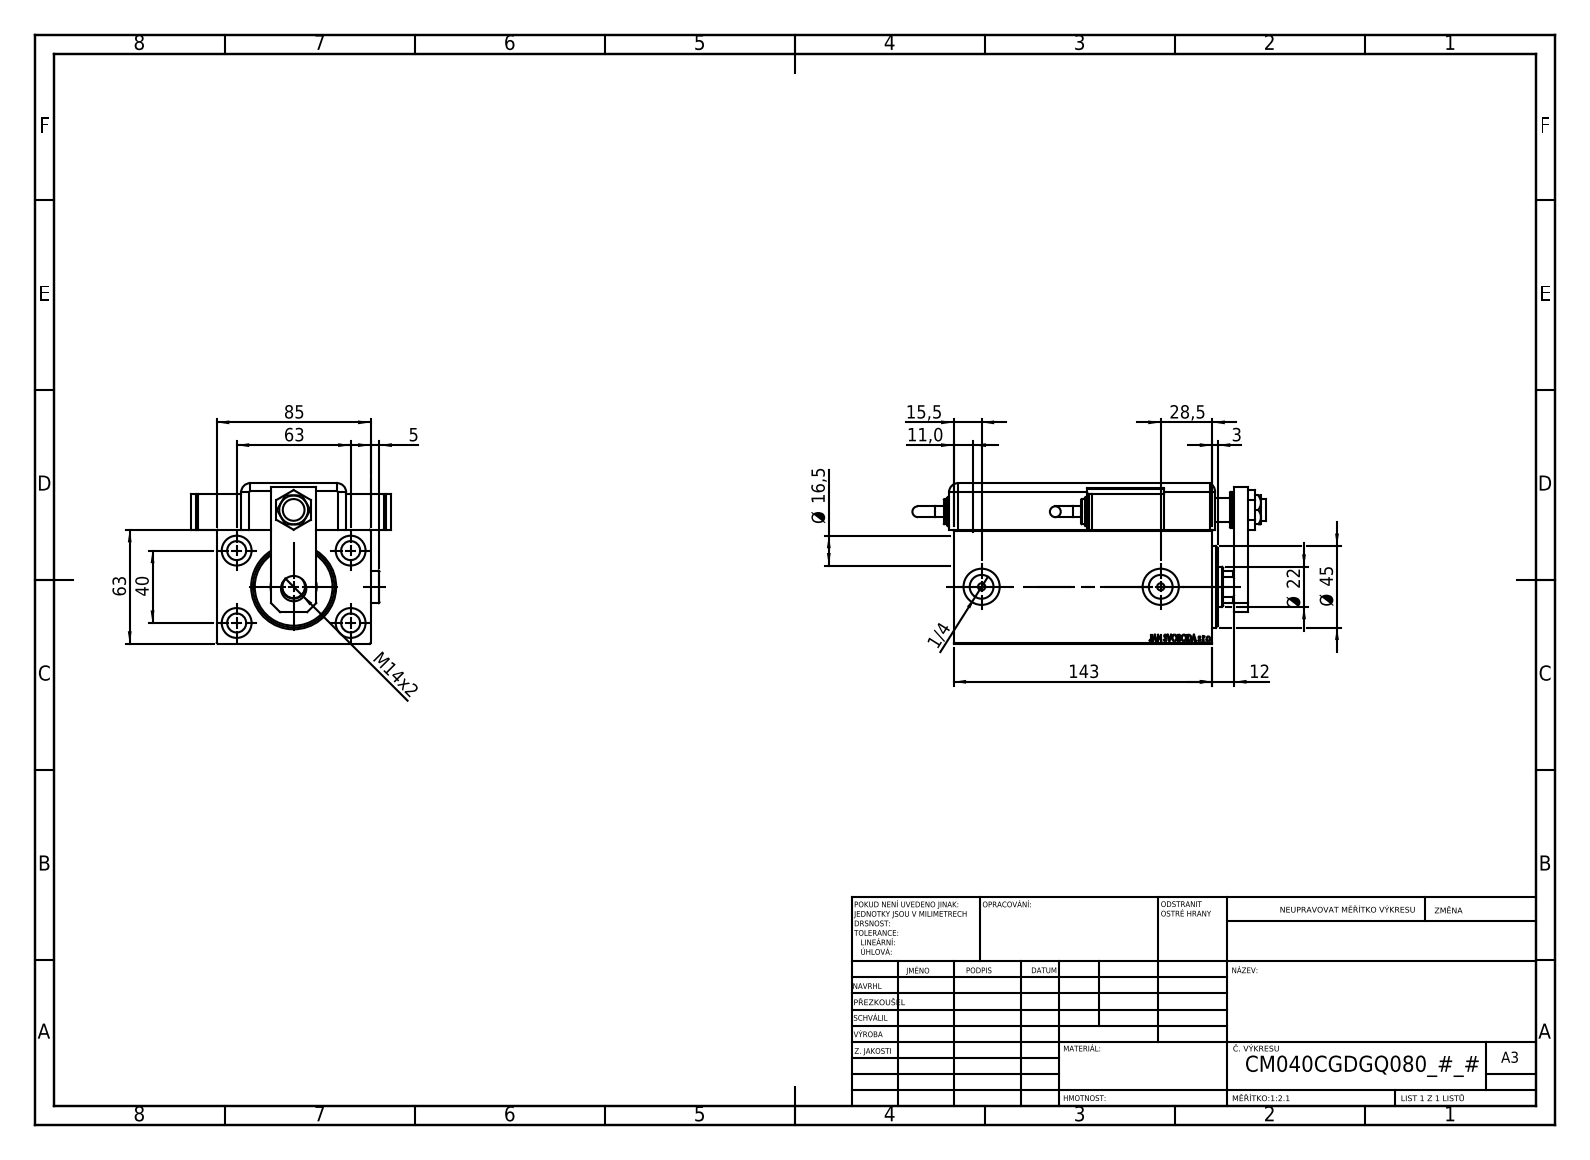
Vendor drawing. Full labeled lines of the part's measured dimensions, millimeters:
Part name (STEP PRODUCT): MAGNETIC SWITCH Q; TYC; V450CM_VC_B; SWITCH DIM A_G (+7 more)
STEP written by: SolidWorks 2019 (CONFIG_CONTROL_DESIGN)
Units: millimetres
Bodies: 15 solids, 1300 faces (648 planar, 131 cylindrical, 521 other)
Overall size (bounding box): 195.46 × 111 × 88.8
Volume: 793 620 mm³ · Surface area: 178 586 mm²
Round holes (diameter × count): ⌀4 ×4, ⌀10.5 ×4, ⌀16.5 ×4, ⌀8 ×2, ⌀13.16 ×2, ⌀14 ×2, ⌀20 ×2, ⌀12 ×1, ⌀12.5 ×1, ⌀13 ×1, ⌀22 ×1, ⌀25.5 ×1
Round bosses / shafts (diameter × count): ⌀20 ×3, ⌀18 ×2, ⌀16 ×2, ⌀14 ×2, ⌀6 ×2
Partial cylindrical surfaces — rounded edges, fillets, slot ends (radius × count): R5 ×9, R10 ×1, R10.5 ×1
Main face-to-face distances: 3, 63, 85, 13.5, 25.8, 88.8, 16.5, 12, 85.8, 22.8
Hole centre spacings: 37.31, 36.79, 37.86, 38.71, 40, 63, 69.99, 74.63
